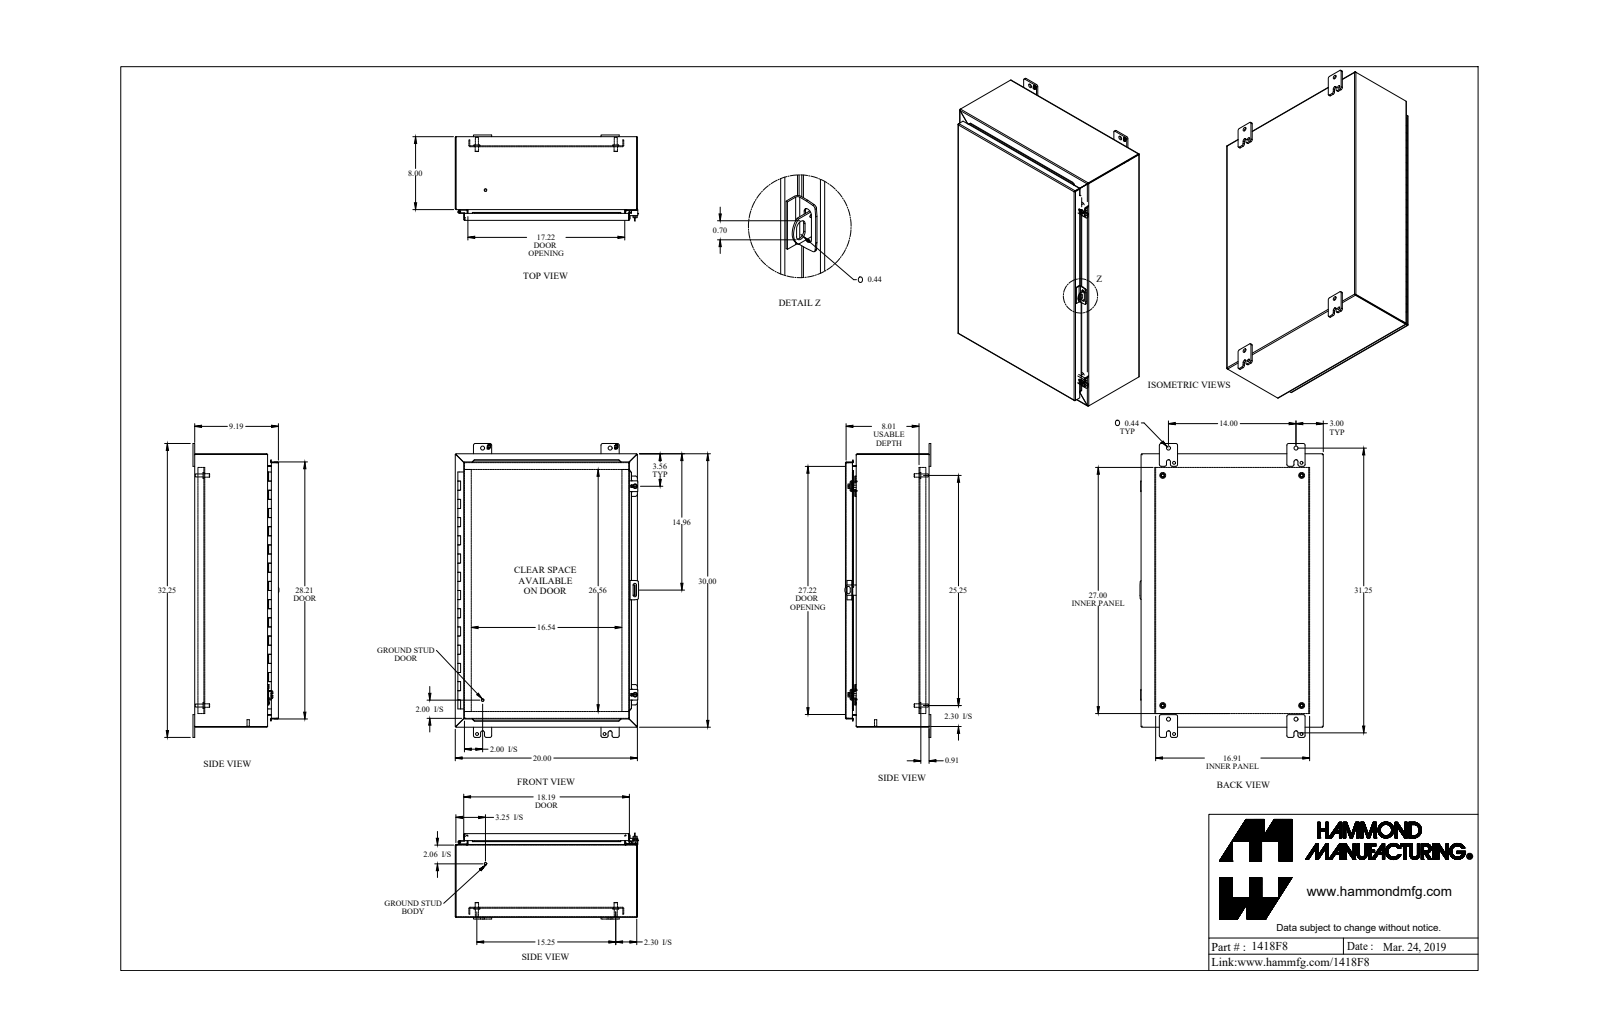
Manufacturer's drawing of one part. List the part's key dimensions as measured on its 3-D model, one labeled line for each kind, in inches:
Part name (STEP PRODUCT): 1418F8
STEP written by: SolidWorks 2019 (AUTOMOTIVE_DESIGN)
Units: inches
Bodies: 37 solids, 985 faces (692 planar, 251 cylindrical, 42 other)
Overall size (bounding box): 32.25 × 20.125 × 9.437
Volume: 576.1 in³ · Surface area: 5 725 in²
Round holes (diameter × count): ⌀0.313 ×4, ⌀0.437 ×4, ⌀0.5 ×4, ⌀0.213 ×2, ⌀0.265 ×2, ⌀0.307 ×2, ⌀0.375 ×2, ⌀0.445 ×2, ⌀0.125 ×1, ⌀0.187 ×1
Round bosses / shafts (diameter × count): ⌀0.65 ×4, ⌀0.375 ×4, ⌀0.33 ×4, ⌀1 ×2, ⌀0.5 ×2, ⌀0.39 ×2, ⌀0.281 ×2, ⌀0.25 ×2
Partial cylindrical surfaces — rounded edges, fillets, slot ends (radius × count): R0.188 ×26, R0.036 ×16, R0.108 ×16, R0.048 ×13, R0.143 ×13, R0.079 ×8, R0.218 ×8, R0.25 ×8
Main face-to-face distances: 0.072, 9.113, 9.185, 0.767, 8.346, 8.418, 0.095, 0.937, 1.009, 19.928
Hole centre spacings: 1.736, 14, 15.25, 29.75, 32.88, 29.498, 29.498, 29.68
